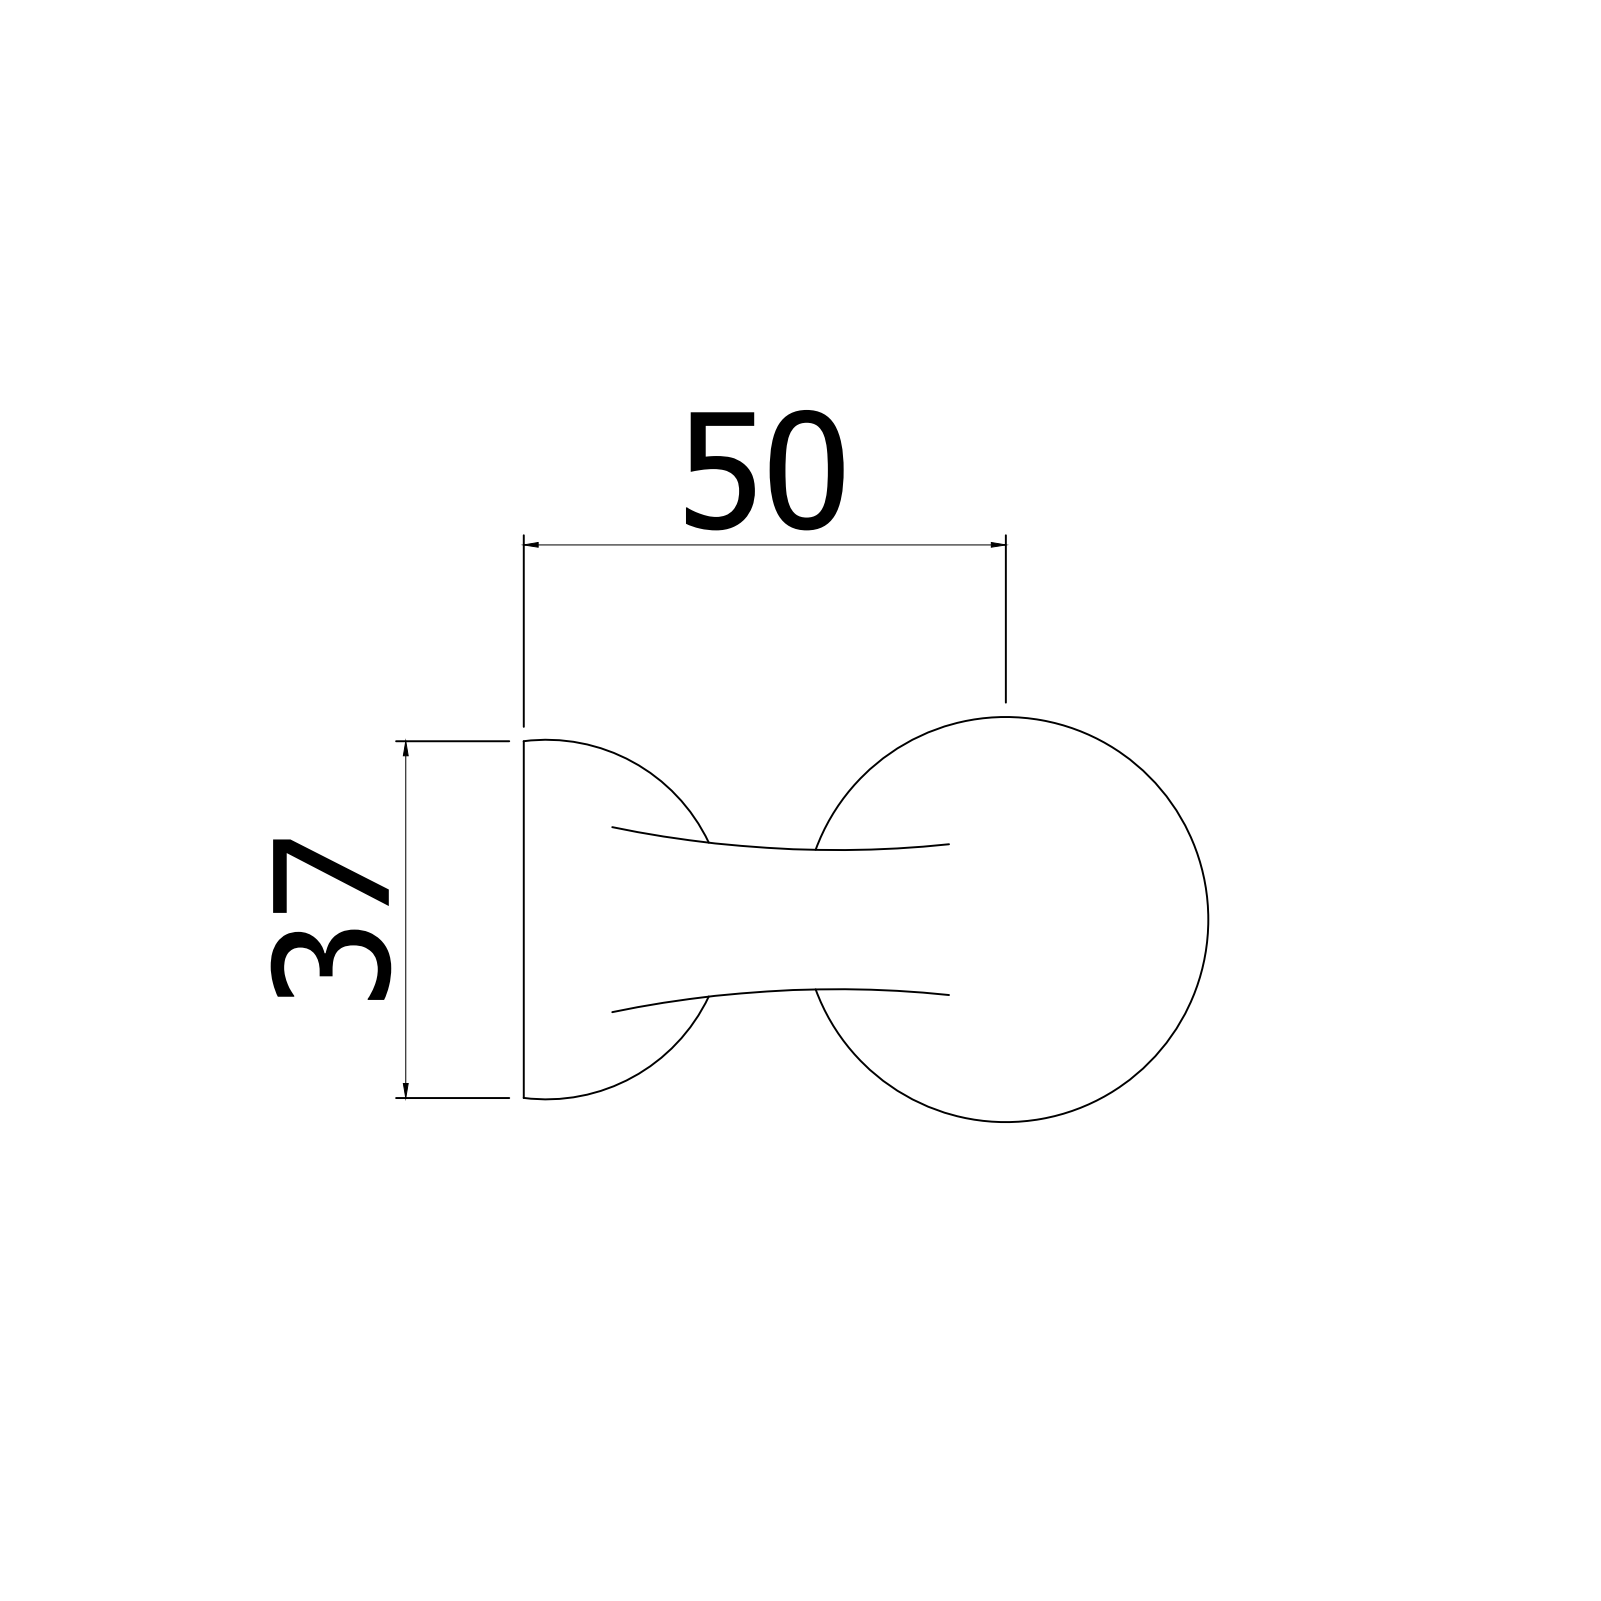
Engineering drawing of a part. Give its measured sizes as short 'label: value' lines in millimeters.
name: ZSUP009CR
written by: CREO PARAMETRIC BY PTC INC, 2020044 (CONFIG_CONTROL_DESIGN)
unit: mm
bodies: 1 solid, 18 faces (3 planar, 0 cylindrical, 15 other)
size: 88.16 × 71 × 42.36
volume: 75 642 mm³; area: 14 779 mm²
face distances: 60.5, 43.5, 17
